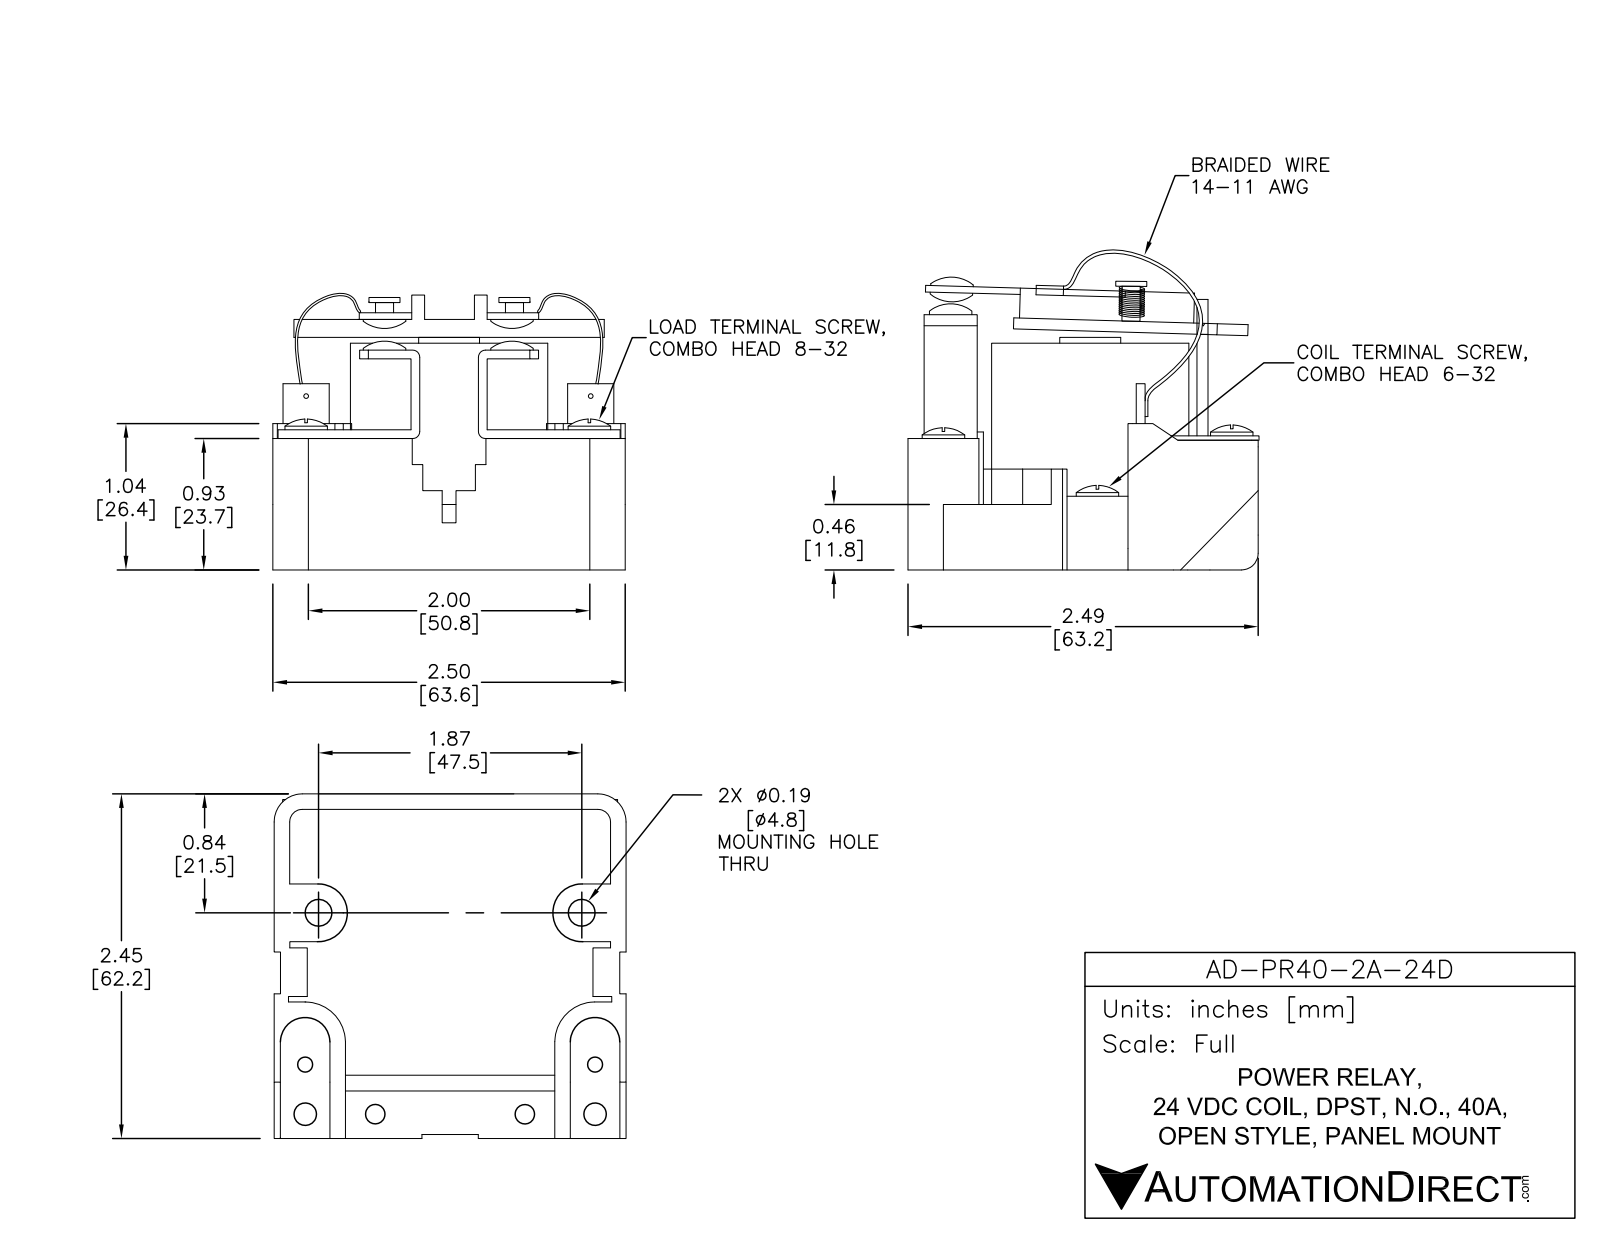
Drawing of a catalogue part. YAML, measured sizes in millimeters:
part_name: "AD-PR40-2A-24D"
step_written_by: "SolidWorks 2018 (AUTOMOTIVE_DESIGN)"
units: millimeters
bodies: {solids: 39, faces: 816, planar: 555, cylindrical: 167, other: 94}
overall_size: [65.57, 64.94, 54.85]
volume: 96384
surface_area: 37339
round_holes:
  - {diameter: 3.33, count: 2}
  - {diameter: 4.8, count: 2}
  - {diameter: 5, count: 2}
  - {diameter: 10, count: 2}
  - {diameter: 30, count: 1}
round_bosses_or_shafts:
  - {diameter: 7.75, count: 4}
  - {diameter: 6.5, count: 4}
  - {diameter: 5.28, count: 4}
  - {diameter: 6.85, count: 2}
  - {diameter: 5.5, count: 2}
  - {diameter: 3.5, count: 2}
  - {diameter: 35.5, count: 1}
  - {diameter: 18, count: 1}
partial_cylinders:
  - {radius: 1, count: 14}
  - {radius: 0.75, count: 10}
  - {radius: 1.5, count: 6}
  - {radius: 3, count: 5}
  - {radius: 5, count: 5}
  - {radius: 0.38, count: 4}
  - {radius: 1.48, count: 4}
  - {radius: 1.51, count: 4}
face_to_face_distances: [2, 48.05, 1, 4.5, 1.5, 36.25, 11.8, 6.5, 44.55, 3.5]
hole_center_spacings: [10, 25.62, 25.71, 35.71, 48.85, 49.86, 29.25, 29.26]
